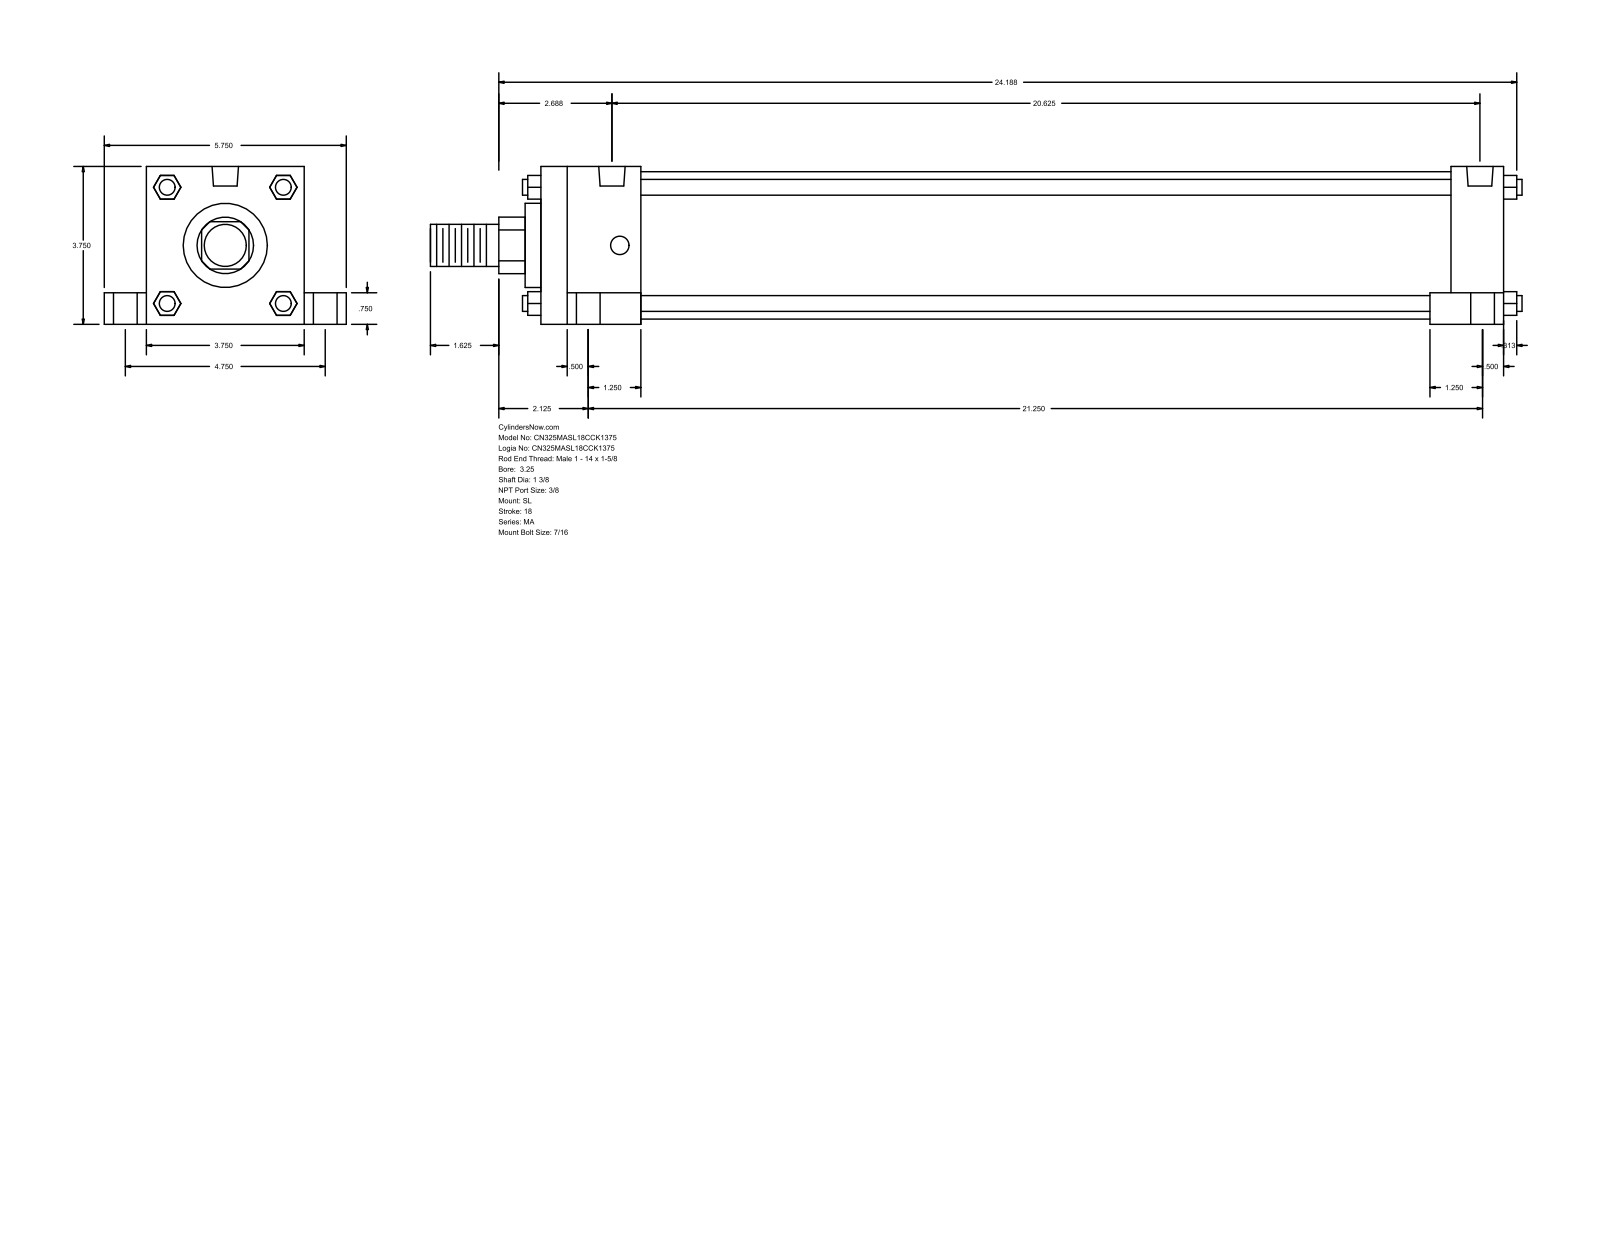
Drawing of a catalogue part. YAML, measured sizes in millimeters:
part_name: "MA_SL__0325_1.375"
step_written_by: "GSSL Pune (CONFIG_CONTROL_DESIGN)"
units: millimeters
bodies: {solids: 0, faces: 148, planar: 112, cylindrical: 36, other: 0}
overall_size: [658.81, 146.05, 95.25]
round_holes:
  - {diameter: 11.11, count: 4}
  - {diameter: 14.29, count: 4}
  - {diameter: 20.64, count: 4}
  - {diameter: 15.93, count: 2}
round_bosses_or_shafts:
  - {diameter: 9.53, count: 4}
  - {diameter: 88.9, count: 1}
  - {diameter: 50.8, count: 1}
  - {diameter: 34.92, count: 1}
  - {diameter: 25.4, count: 1}
partial_cylinders:
  - {radius: 17.06, count: 1}
face_to_face_distances: [95.24, 581.02, 488.95, 25.41, 120.65, 549.27, 31.75, 60.32, 520.7, 19.05]
hole_center_spacings: [60.35, 60.66, 62, 63.27, 120.66, 514.35, 524.18, 528.92]
